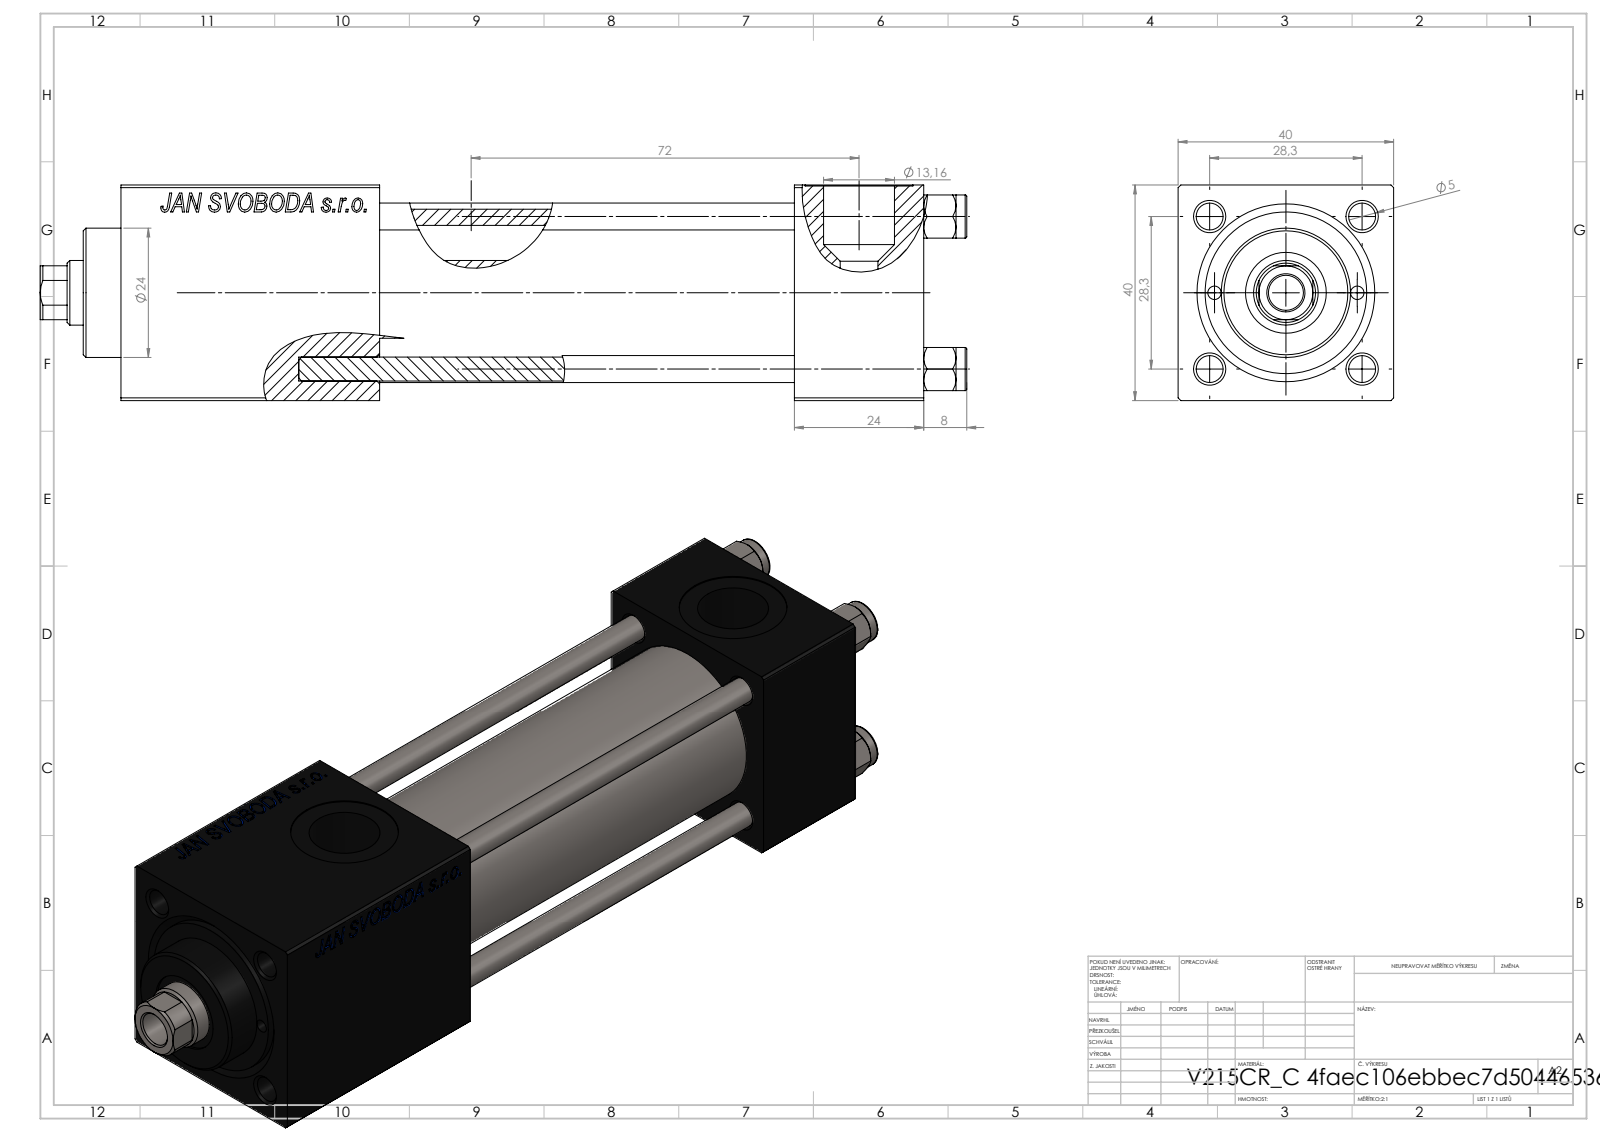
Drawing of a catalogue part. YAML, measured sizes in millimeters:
part_name: "NUT_M5_C; V215CR_VCP_C; V215CR_C_TYCINKA; V215_VC_A (+1 more)"
step_written_by: "SolidWorks 2019 (CONFIG_CONTROL_DESIGN)"
units: millimeters
bodies: {solids: 11, faces: 1154, planar: 527, cylindrical: 91, other: 536}
overall_size: [172, 40, 40]
volume: 155925
surface_area: 62815
round_holes:
  - {diameter: 5, count: 4}
  - {diameter: 20, count: 3}
  - {diameter: 2.5, count: 2}
  - {diameter: 7, count: 2}
  - {diameter: 13.16, count: 2}
  - {diameter: 6.5, count: 1}
  - {diameter: 12, count: 1}
  - {diameter: 15, count: 1}
  - {diameter: 25, count: 1}
  - {diameter: 30, count: 1}
round_bosses_or_shafts:
  - {diameter: 8, count: 4}
  - {diameter: 31, count: 1}
  - {diameter: 24, count: 1}
partial_cylinders:
  - {radius: 5.5, count: 1}
face_to_face_distances: [40, 24, 120.3, 96.3, 48, 101, 77, 19.3, 149, 125]
hole_center_spacings: [14.18, 20.01, 28.3, 30.84, 13.25, 40.02, 26.5, 102]
